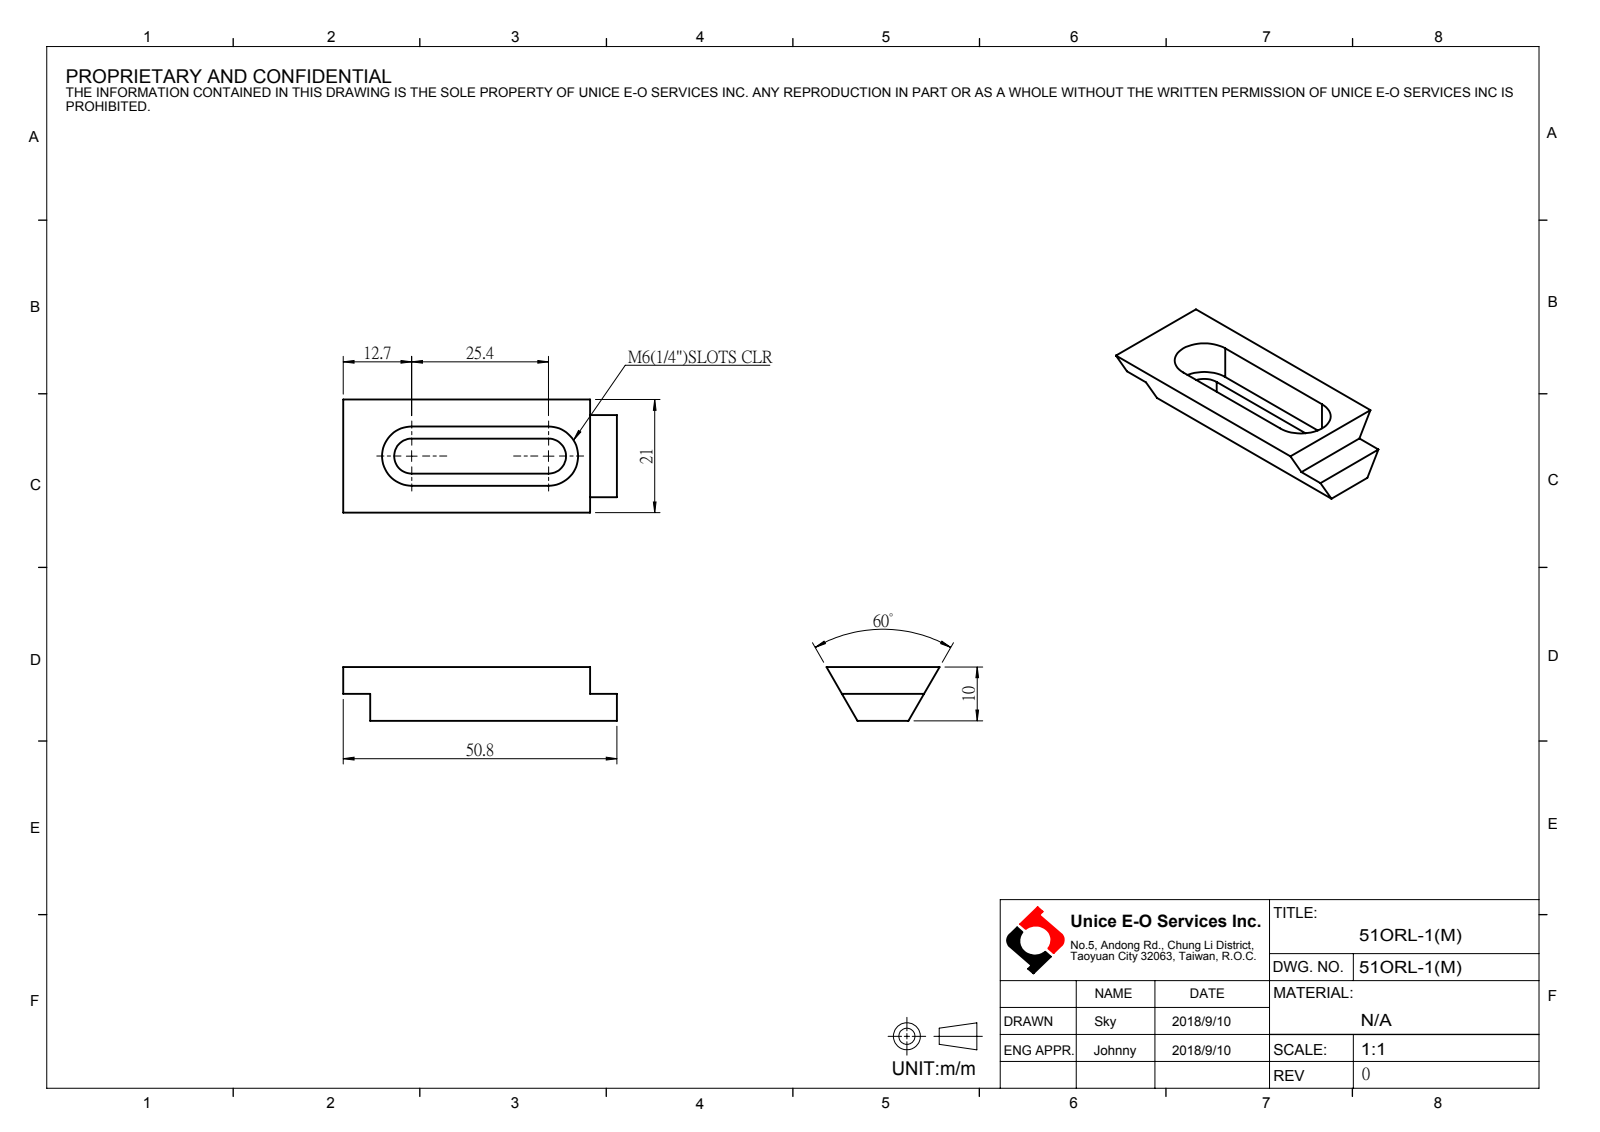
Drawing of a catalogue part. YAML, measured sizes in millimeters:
part_name: "51ORL-1(M)"
step_written_by: "SolidWorks 2016 (AUTOMOTIVE_DESIGN)"
units: millimeters
bodies: {solids: 0, faces: 21, planar: 15, cylindrical: 6, other: 0}
overall_size: [50.8, 21, 10]
partial_cylinders:
  - {radius: 3.25, count: 2}
  - {radius: 5.5, count: 2}
face_to_face_distances: [5, 6.5, 10, 2.25, 8.75, 3.5, 11, 45.8, 1.5, 50.8]
